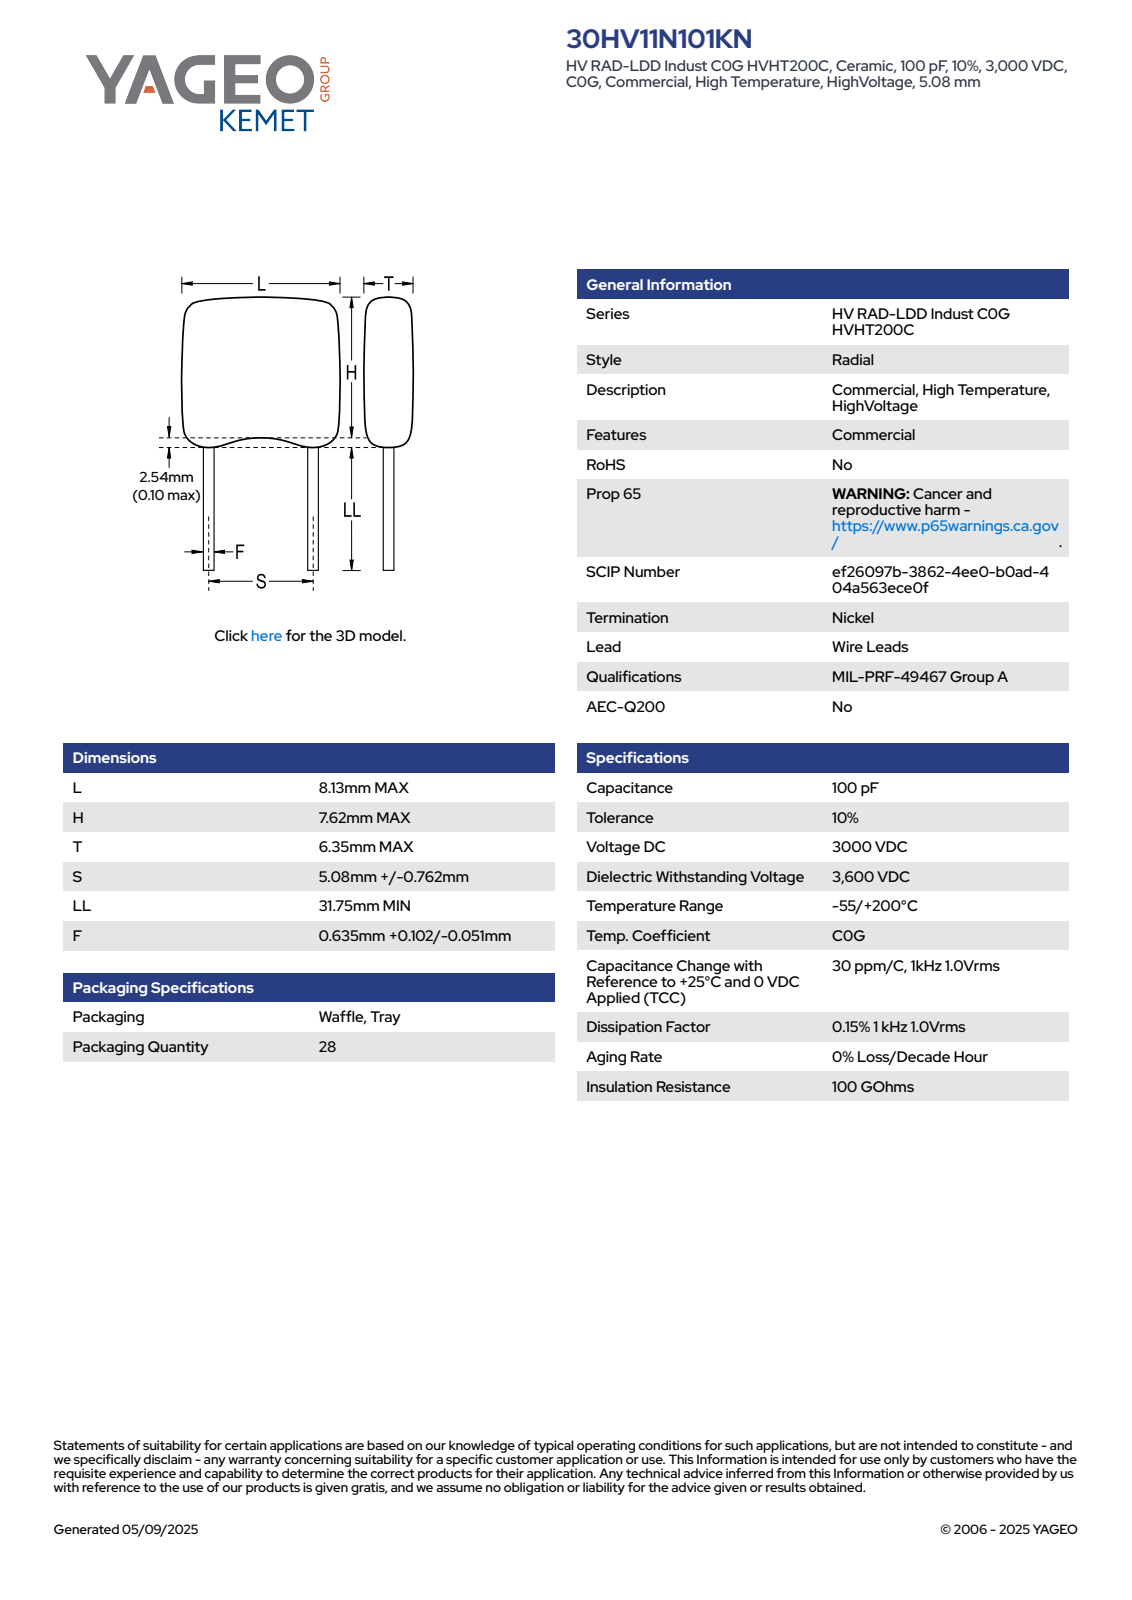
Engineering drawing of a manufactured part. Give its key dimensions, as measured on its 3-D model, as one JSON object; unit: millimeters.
{"part_name": "CCRM_RCST_HV11_L8.13H7.62T6.35S5.08LL3.175F0.737", "step_written_by": "SolidWorks 2021 (AUTOMOTIVE_DESIGN)", "units": "millimeters", "bodies": {"solids": 4, "faces": 92, "planar": 66, "cylindrical": 16, "other": 10}, "overall_size": [40.89, 8.13, 5.08], "volume_mm3": 346, "surface_area_mm2": 416, "round_bosses_or_shafts": [[0.64, 2]], "partial_cylinders_radius": [[0.5, 8], [2, 4]], "face_to_face_distances": [5.08, 8.13, 9.14, 31.75, 40.89, 36.96, 5.21, 3.93, 35.67, 3.92]}
